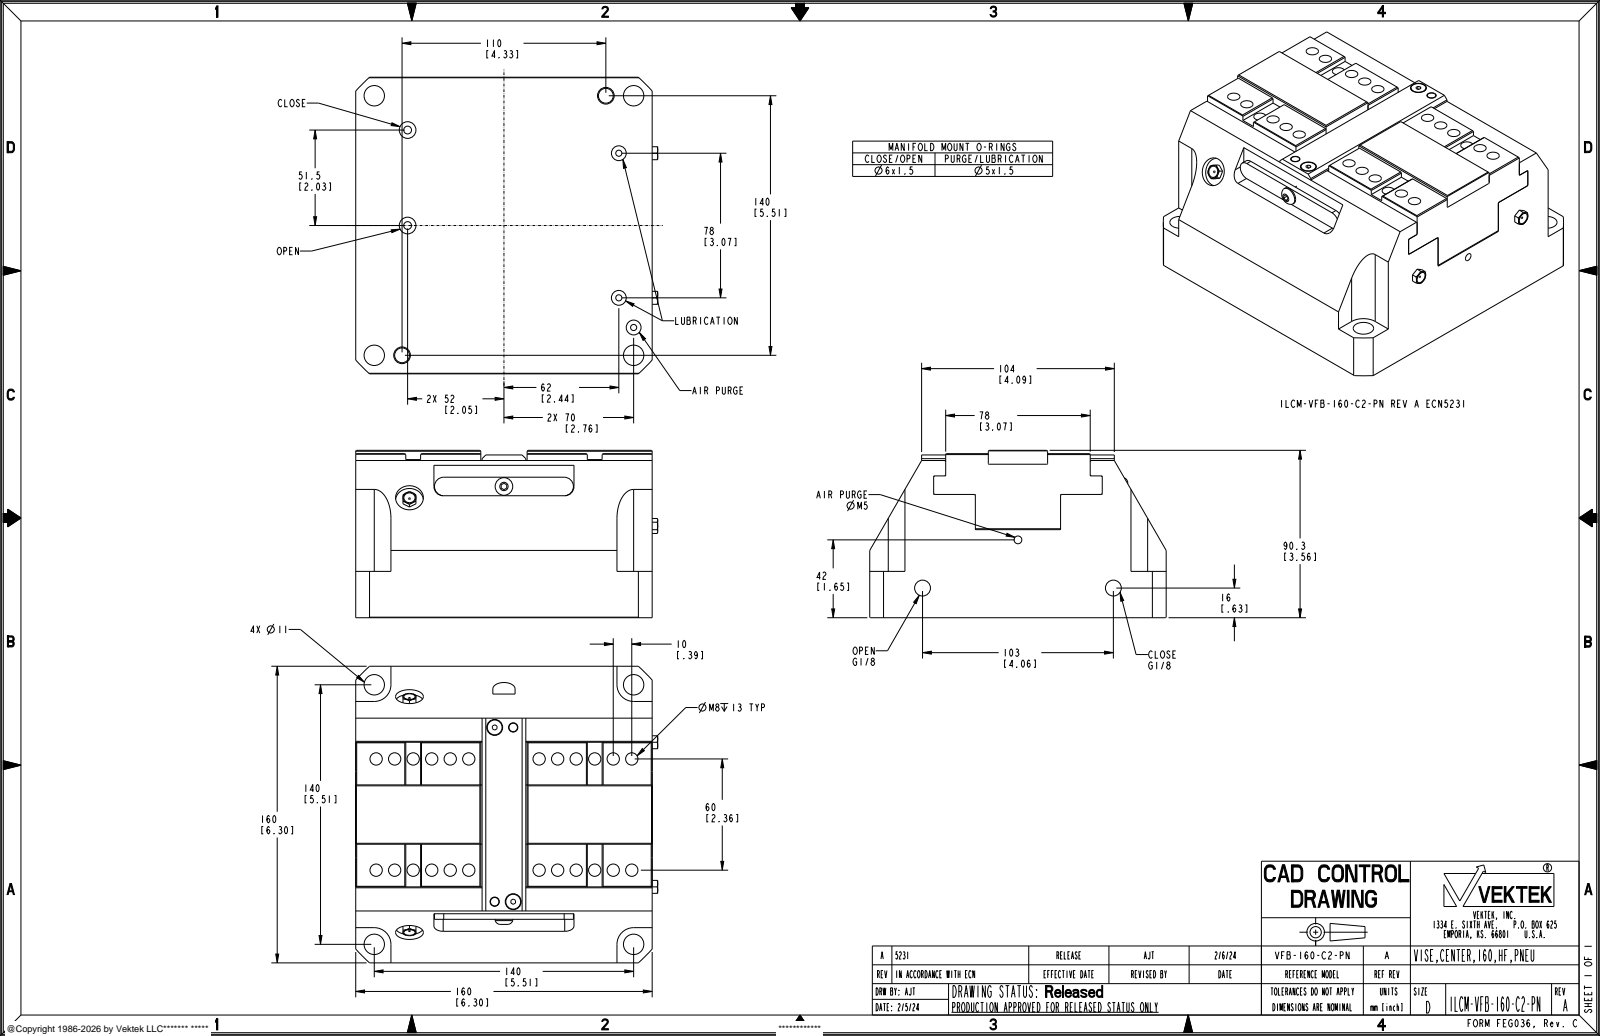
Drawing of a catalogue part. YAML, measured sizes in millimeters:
part_name: "CORPO; GRIFFA; COPERCHIO; ISO_2338_-_5_H8_X_10_-_B (+4 more)"
step_written_by: "CREO PARAMETRIC BY PTC INC, 2021164 (AUTOMOTIVE_DESIGN)"
units: millimeters
bodies: {solids: 10, faces: 593, planar: 270, cylindrical: 165, other: 158}
overall_size: [163, 160, 90.3]
volume: 1895000
surface_area: 183634
round_holes:
  - {diameter: 6.65, count: 24}
  - {diameter: 3.3, count: 5}
  - {diameter: 8, count: 5}
  - {diameter: 4.2, count: 4}
  - {diameter: 11, count: 4}
  - {diameter: 4, count: 2}
  - {diameter: 5, count: 2}
  - {diameter: 8.57, count: 2}
  - {diameter: 9, count: 2}
  - {diameter: 15, count: 2}
  - {diameter: 4.13, count: 1}
  - {diameter: 5.2, count: 1}
round_bosses_or_shafts:
  - {diameter: 8, count: 2}
  - {diameter: 9.5, count: 1}
  - {diameter: 5, count: 1}
partial_cylinders:
  - {radius: 0.4, count: 10}
  - {radius: 2.6, count: 4}
  - {radius: 3.6, count: 4}
  - {radius: 5, count: 4}
  - {radius: 9, count: 4}
  - {radius: 6, count: 1}
  - {radius: 108, count: 1}
face_to_face_distances: [19, 66.5, 160, 47.5, 41, 57, 103, 18.3, 84.8, 37.3]
hole_center_spacings: [10, 60.83, 20, 63.25, 47.16, 60, 88.68, 30]
